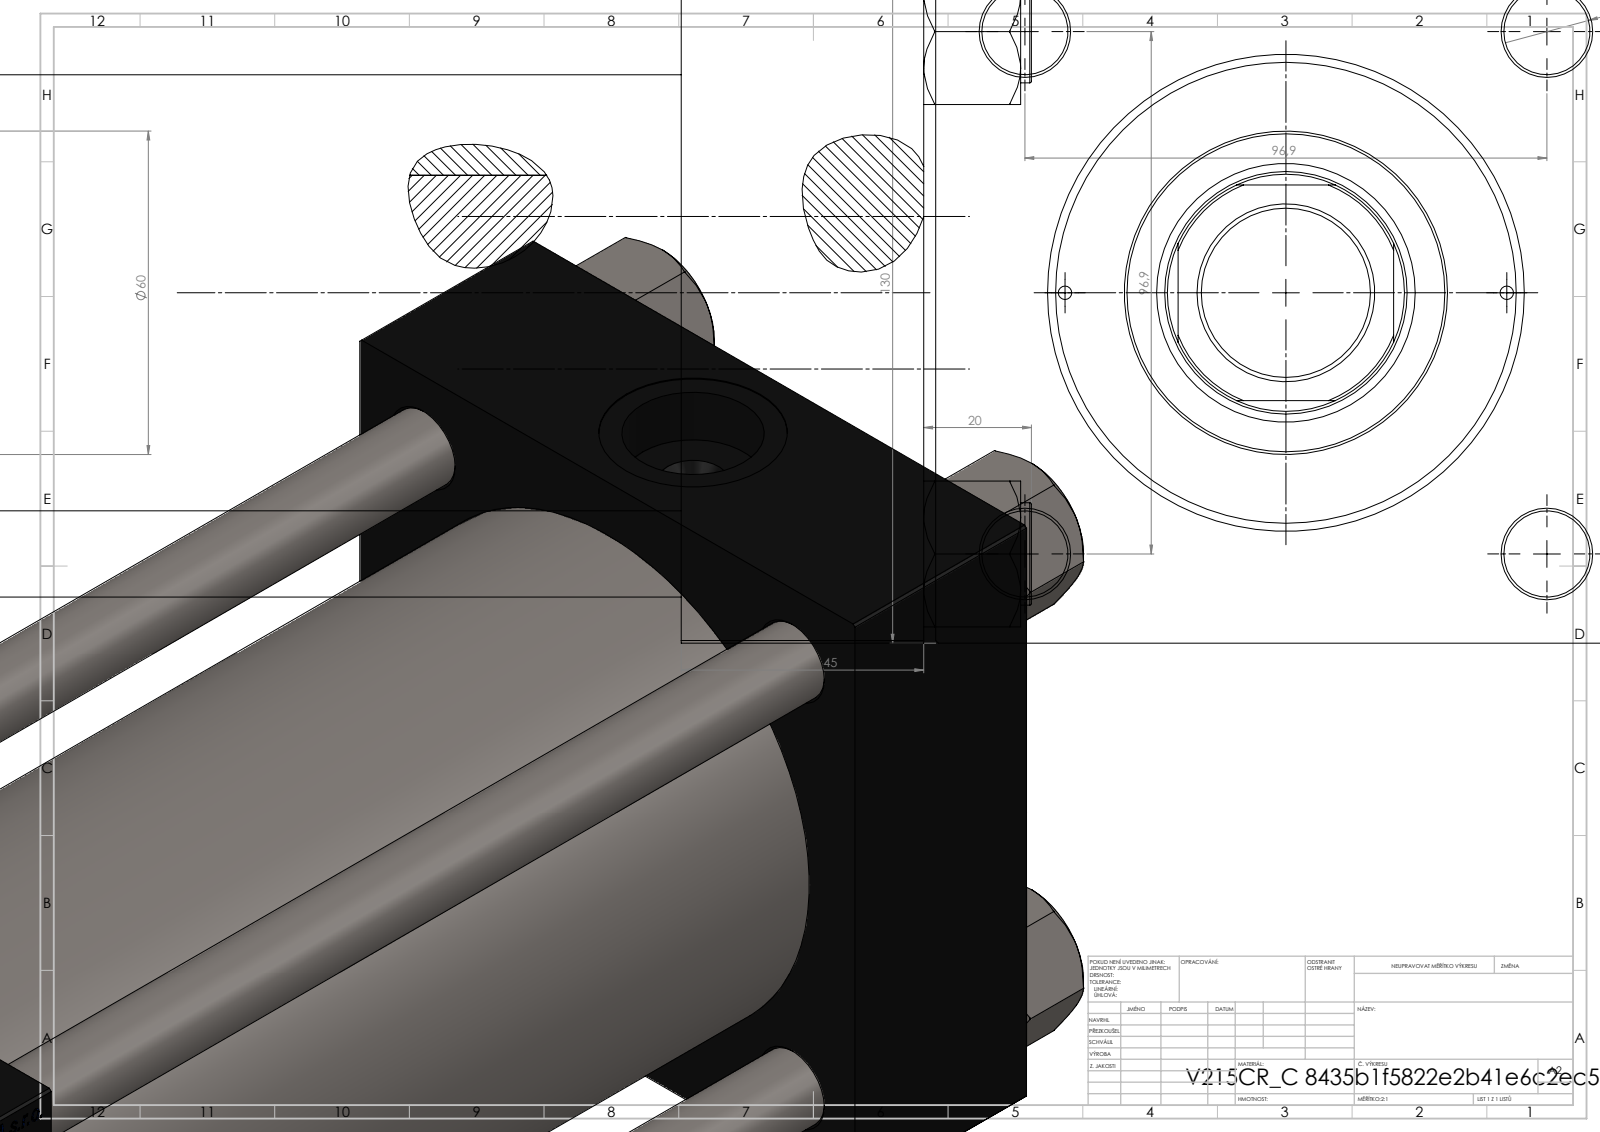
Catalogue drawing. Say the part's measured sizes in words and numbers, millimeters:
The part is named "V215CR_C_Body; NUT_M5_C; V215CR_C_TYCINKA; V215_VC_A (+2 more)". Its 3-D file was written by "SolidWorks 2019 (CONFIG_CONTROL_DESIGN)". It is 12 solids with 1217 faces: 580 planar, 95 cylindrical and 542 other. Overall it measures 428 by 130 by 130 millimeters. Its volume is 2 934 000 cubic millimeters and its surface area 471 483 square millimeters. Round holes: 4 of diameter 16, 2 of diameter 2.5, 2 of diameter 7, 2 of diameter 26.44, 2 of diameter 35, 1 of diameter 31.5, 1 of diameter 45, 1 of diameter 48, 1 of diameter 76, 1 of diameter 85.5, 1 of diameter 100. Round bosses or shafts: 4 of diameter 19, 1 of diameter 106, 1 of diameter 60, 1 of diameter 33, 1 of diameter 31. Partial cylindrical surfaces (rounded edges, fillets, slot ends): 1 of radius 22. The main face-to-face distances are 130, 45, 328, 283, 256, 211, 72, 96, 51, 160. The hole center spacings are 49.02, 68.52, 96.9, 101.73, 41, 137.04, 82, 258.5.
